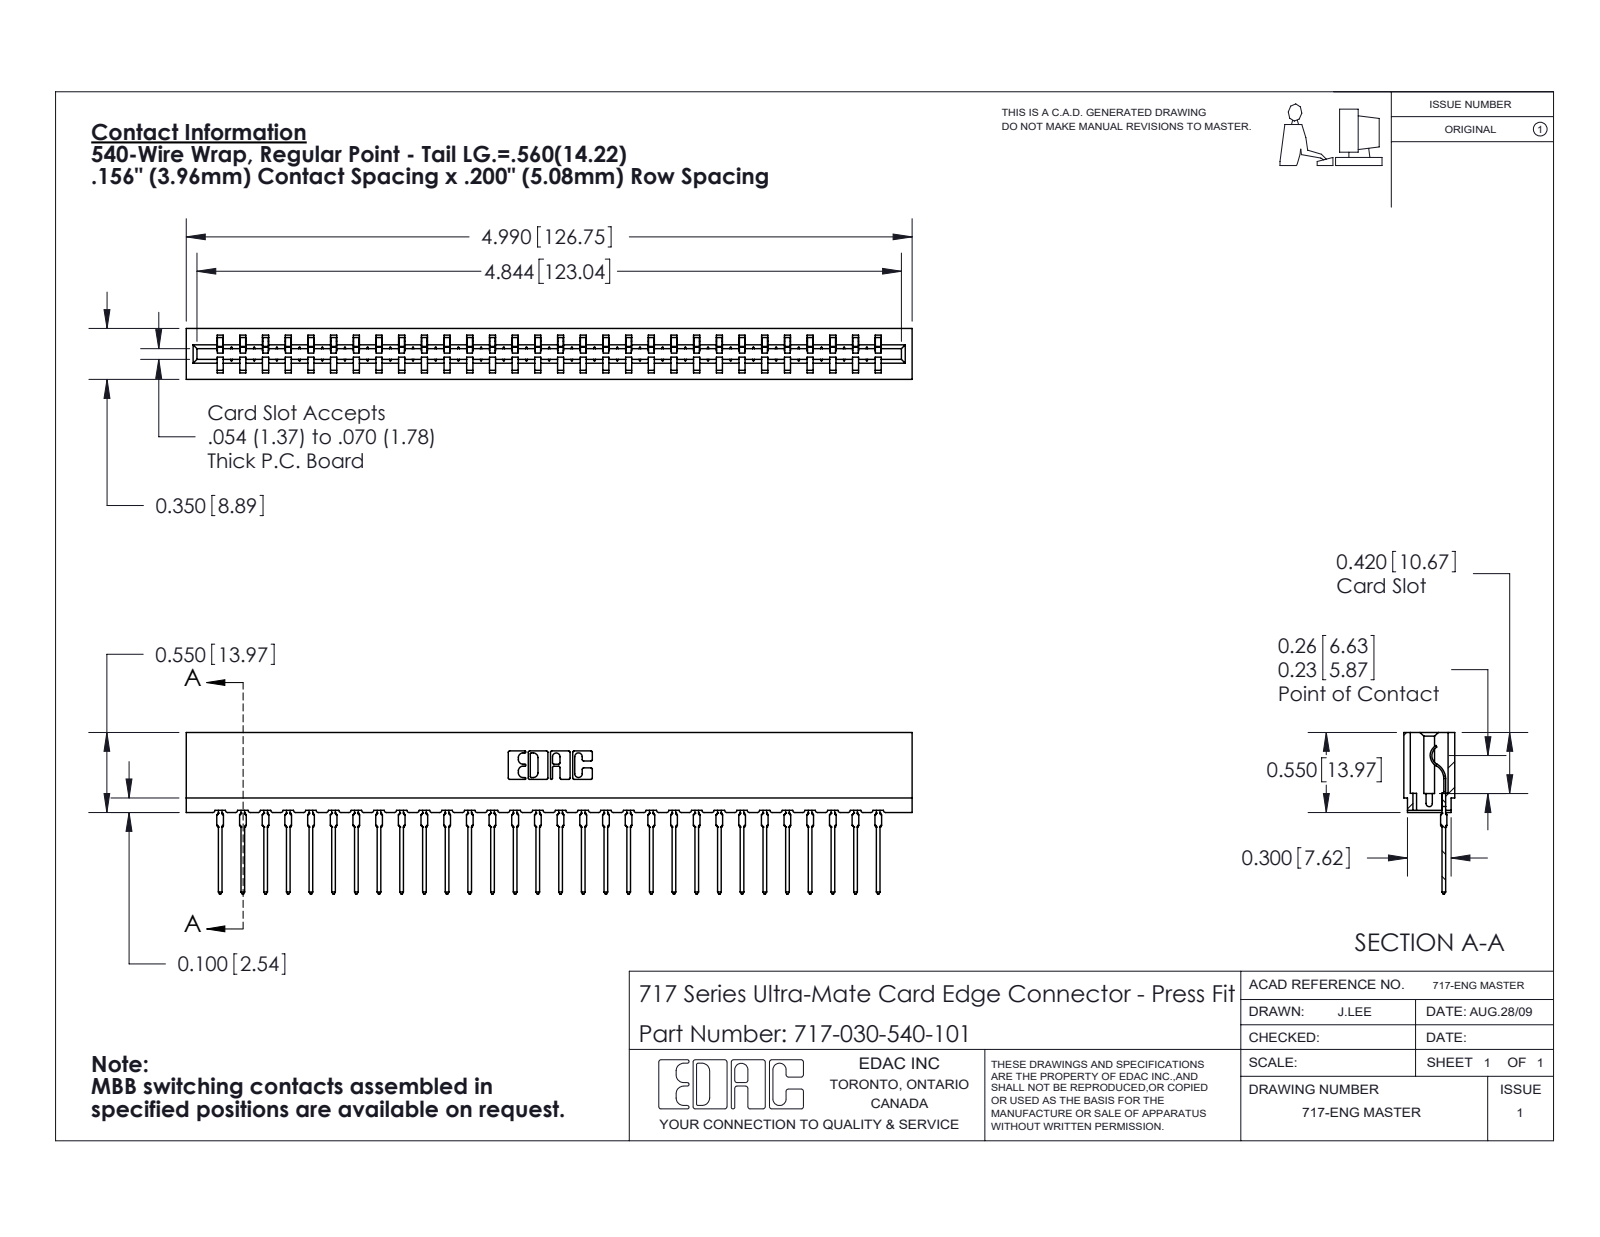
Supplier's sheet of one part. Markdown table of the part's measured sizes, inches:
| quantity | value |
| --- | --- |
| part name | 745-292-001_540; 717 Part_Insulator Option - 06; 717-030-540-101 |
| STEP written by | SolidWorks 2020 (CONFIG_CONTROL_DESIGN) |
| units | inches |
| bodies | 31 solids, 3484 faces (2094 planar, 610 cylindrical, 780 other) |
| overall size | 4.99 × 1.109 × 0.35 |
| volume | 0.661 in³ |
| surface area | 23.91 in² |
| partial cylindrical surfaces (radius × count) | 0.015 × 60, 0.021 × 60, 0.01 × 22, 0.007 × 6, 0.031 × 6, 0.005 × 4, 0.011 × 4, 0.026 × 3 |
| main face-to-face distances | 0.212, 0.138, 0.35, 0.074, 0.156, 0.063, 0.287, 0.076, 0.149, 0.045 |
